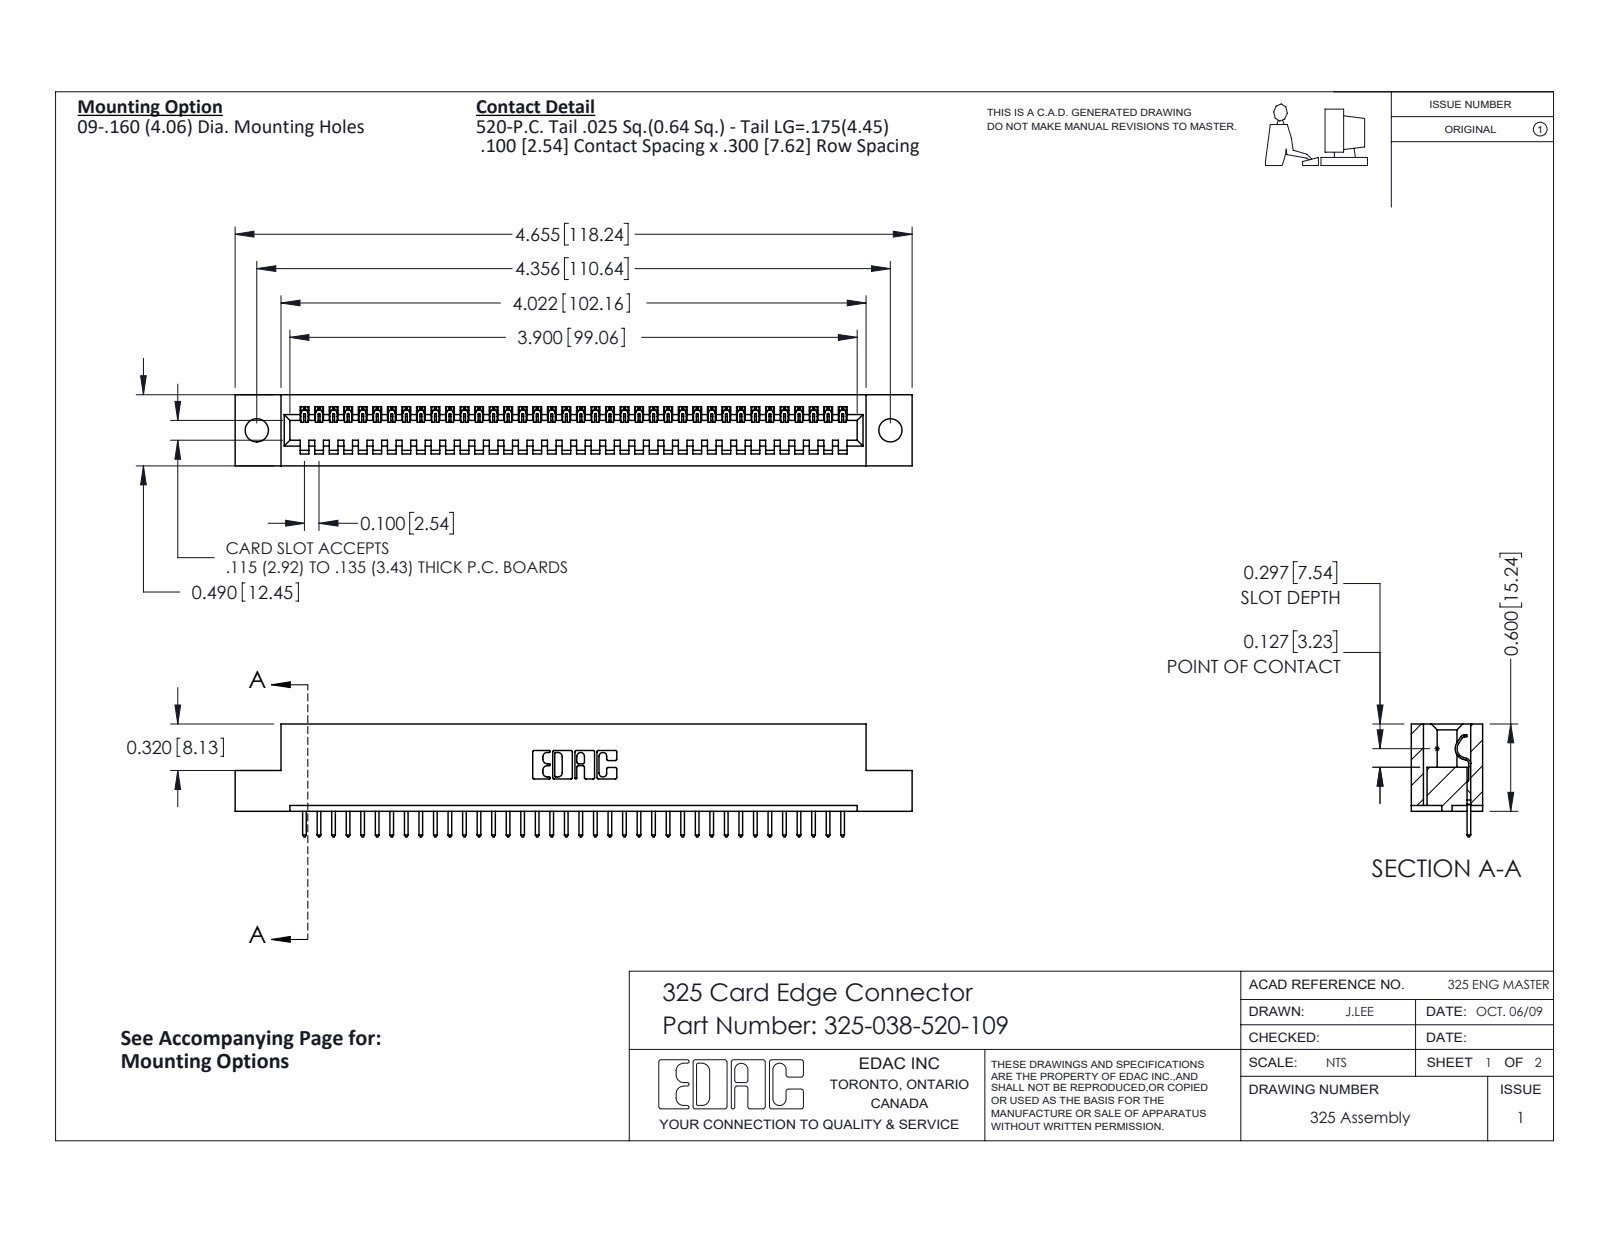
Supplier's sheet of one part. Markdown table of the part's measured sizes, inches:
| quantity | value |
| --- | --- |
| part name | 325 Part_.160 TH; 325-038-520-109; 325-292-001_325-293-120 |
| STEP written by | SolidWorks 2016 (CONFIG_CONTROL_DESIGN) |
| units | inches |
| bodies | 39 solids, 2318 faces (1666 planar, 652 cylindrical, 0 other) |
| overall size | 4.655 × 0.775 × 0.49 |
| volume | 0.894 in³ |
| surface area | 23.92 in² |
| round holes (diameter × count) | 0.16 × 2 |
| partial cylindrical surfaces (radius × count) | 0.006 × 76, 0.01 × 76, 0.01 × 22, 0.007 × 6, 0.031 × 6, 0.026 × 3, 0.014 × 1, 0.022 × 1 |
| main face-to-face distances | 0.083, 0.407, 0.49, 0.3, 0.107, 0.383, 0.025, 0.325, 0.56, 0.263 |
| hole center spacings | 4.356 |
